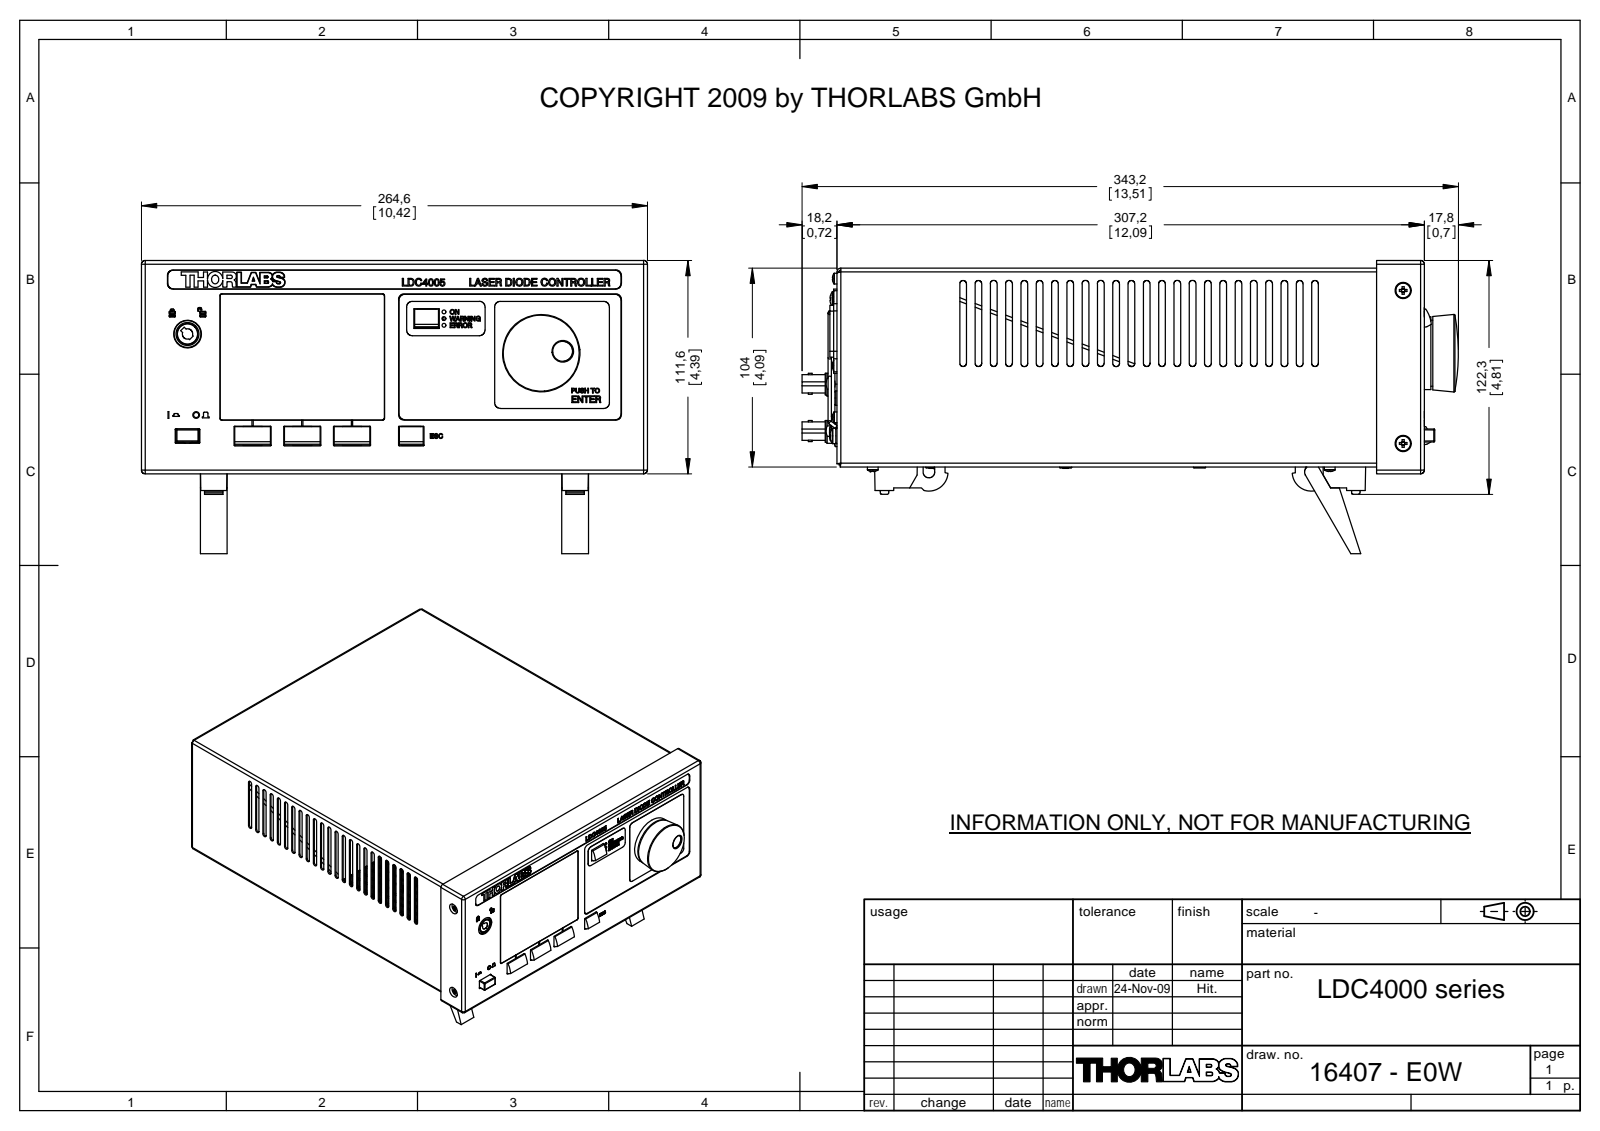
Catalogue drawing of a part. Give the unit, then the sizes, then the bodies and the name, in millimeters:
Units: millimetres
Overall size (bounding box): 343.2 × 264.6 × 153.3
Round holes (diameter × count): ⌀1.1 ×8, ⌀8.1 ×6, ⌀0.8 ×4, ⌀3.5 ×4, ⌀8.5 ×4, ⌀1 ×3, ⌀3.6 ×3, ⌀3.7 ×3, ⌀2.3 ×2, ⌀2.5 ×2, ⌀14.5 ×2, ⌀4 ×1
Round bosses / shafts (diameter × count): ⌀1.8 ×16, ⌀5.6 ×8, ⌀11.6 ×6, ⌀9.7 ×6, ⌀8 ×4, ⌀6.3 ×3, ⌀4.7 ×3, ⌀2 ×3
Partial cylindrical surfaces — rounded edges, fillets, slot ends (radius × count): R0.8 ×87, R1.8 ×48, R0.3 ×21, R2 ×19, R0.5 ×17, R3 ×10, R0.3 ×6, R6.4 ×6
Main face-to-face distances: 1, 1.5, 103, 102, 100.5, 101.5, 8, 92.5, 93.5, 9.5
Hole centre spacings: 2.8, 2.9, 19, 31.2, 2.9, 4.9, 10, 24.7
Bodies: 0 solids, 2644 faces (1527 planar, 718 cylindrical, 399 other)
Part name (STEP PRODUCT): 16407-E0W
STEP written by: SolidWorks 2009 (CONFIG_CONTROL_DESIGN)
